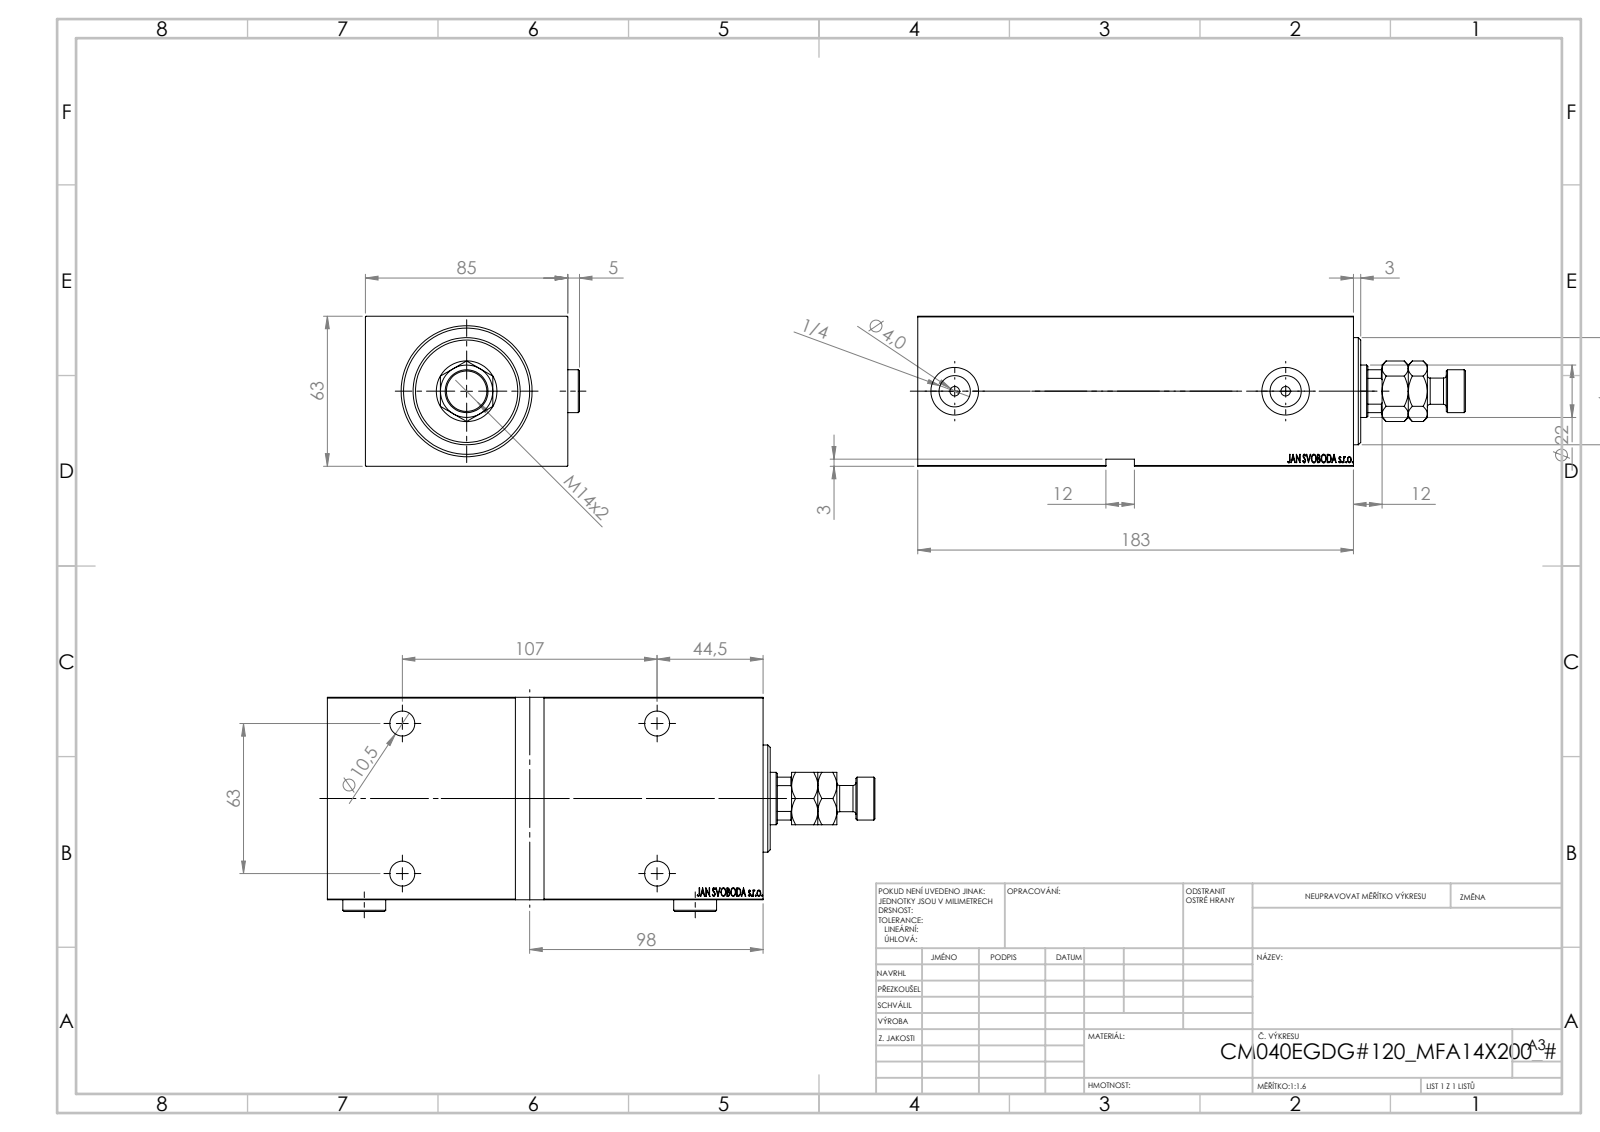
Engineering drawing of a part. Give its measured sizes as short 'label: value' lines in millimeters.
name: V450CM_E_VCP; Zatka_OIL_PORT; V450CM_E_Body; V450CM_VC_B (+1 more)
written by: SolidWorks 2019 (CONFIG_CONTROL_DESIGN)
unit: mm
bodies: 6 solids, 964 faces (462 planar, 72 cylindrical, 430 other)
size: 230 × 89.9 × 63
volume: 856 990 mm³; area: 129 085 mm²
holes: 4× ⌀10.5, 4× ⌀16.5, 2× ⌀4, 2× ⌀13.16, 2× ⌀20, 1× ⌀12.5, 1× ⌀22, 1× ⌀25.5, 1× ⌀40, 1× ⌀53
bosses: 3× ⌀18, 1× ⌀45, 1× ⌀42, 1× ⌀11
rounds: 1× R10.5
face distances: 63, 85, 183, 12, 171, 5, 3, 166, 178, 84.9
hole spacings: 63, 107, 124.17, 139
